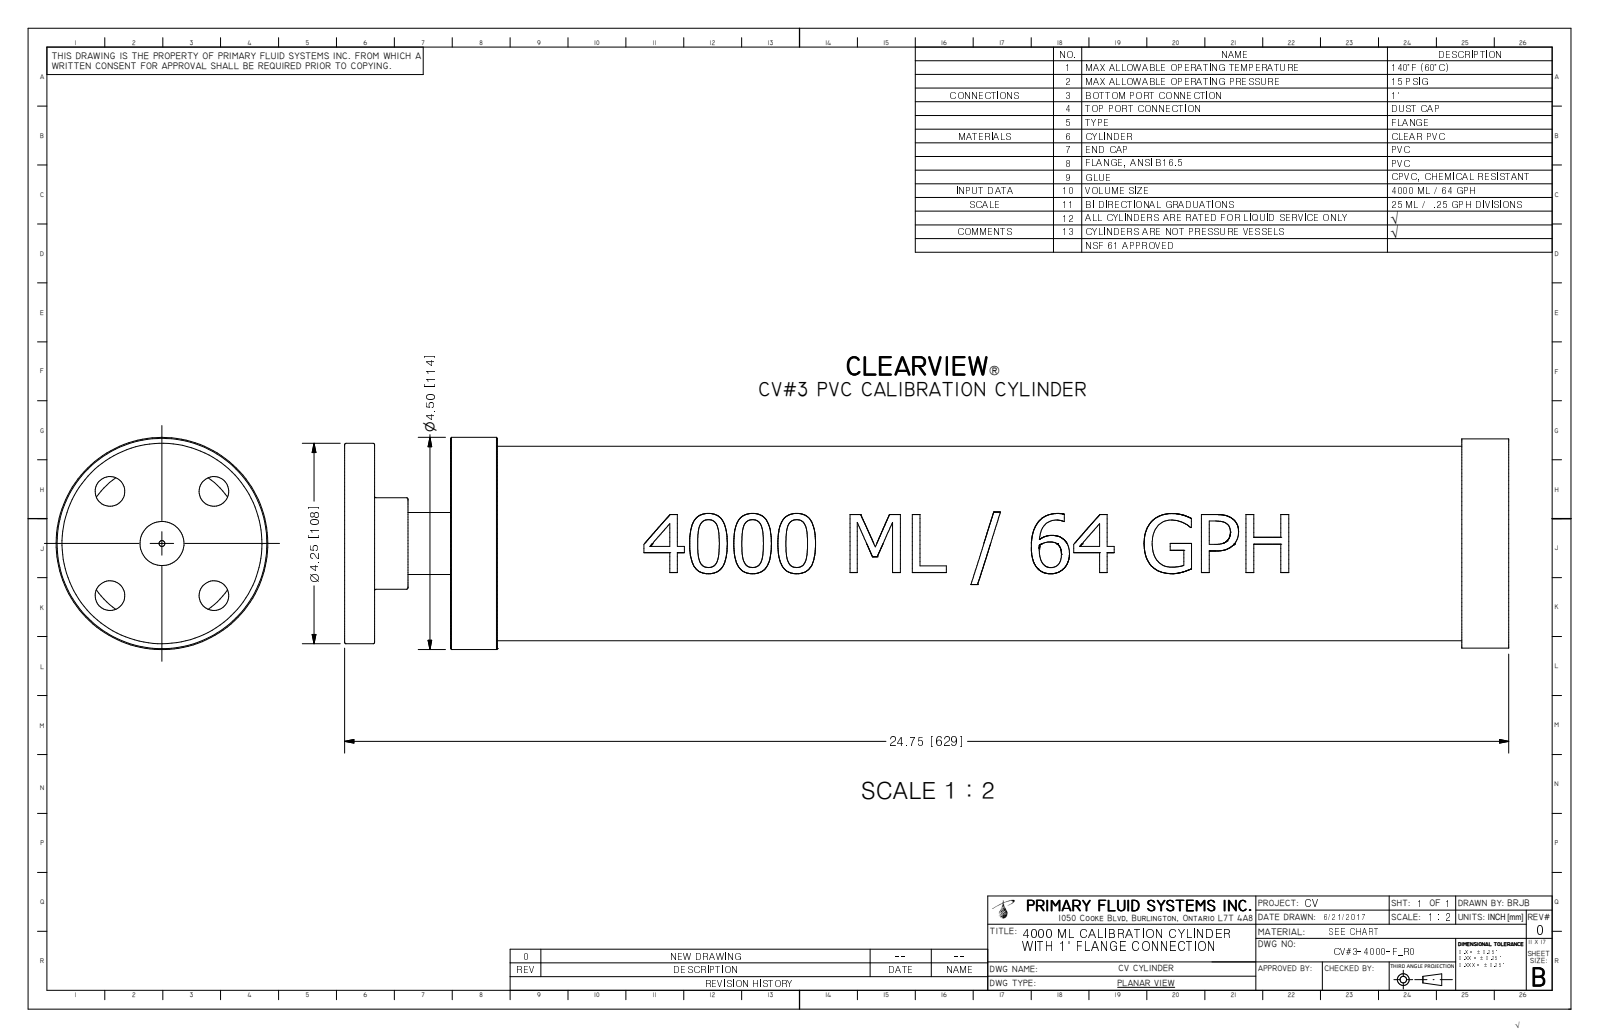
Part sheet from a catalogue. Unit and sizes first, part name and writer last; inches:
Units: inches
Overall size (bounding box): 24.75 × 4.5 × 4.5
Round holes (diameter × count): ⌀0.63 ×4, ⌀0.936 ×1, ⌀0.957 ×1, ⌀1.156 ×1, ⌀4.005 ×1, ⌀4.15 ×1
Round bosses / shafts (diameter × count): ⌀4.5 ×1, ⌀4.437 ×1, ⌀4.25 ×1, ⌀4.125 ×1, ⌀3.965 ×1, ⌀3.876 ×1, ⌀1.941 ×1, ⌀1.315 ×1
Partial cylindrical surfaces — rounded edges, fillets, slot ends (radius × count): R2.061 ×1
Main face-to-face distances: 1, 23.75, 24.75, 0.635, 23.115, 24.115, 21.5, 2.25, 1.615, 22.5
Hole centre spacings: 1.562, 2.209, 3.125
Volume: 52.27 in³ · Surface area: 723.5 in²
Bodies: 1 solid, 274 faces (98 planar, 36 cylindrical, 140 other)
Part name (STEP PRODUCT): PV#3-4000-F_R0
STEP written by: Autodesk Inventor 2009 (AUTOMOTIVE_DESIGN)
